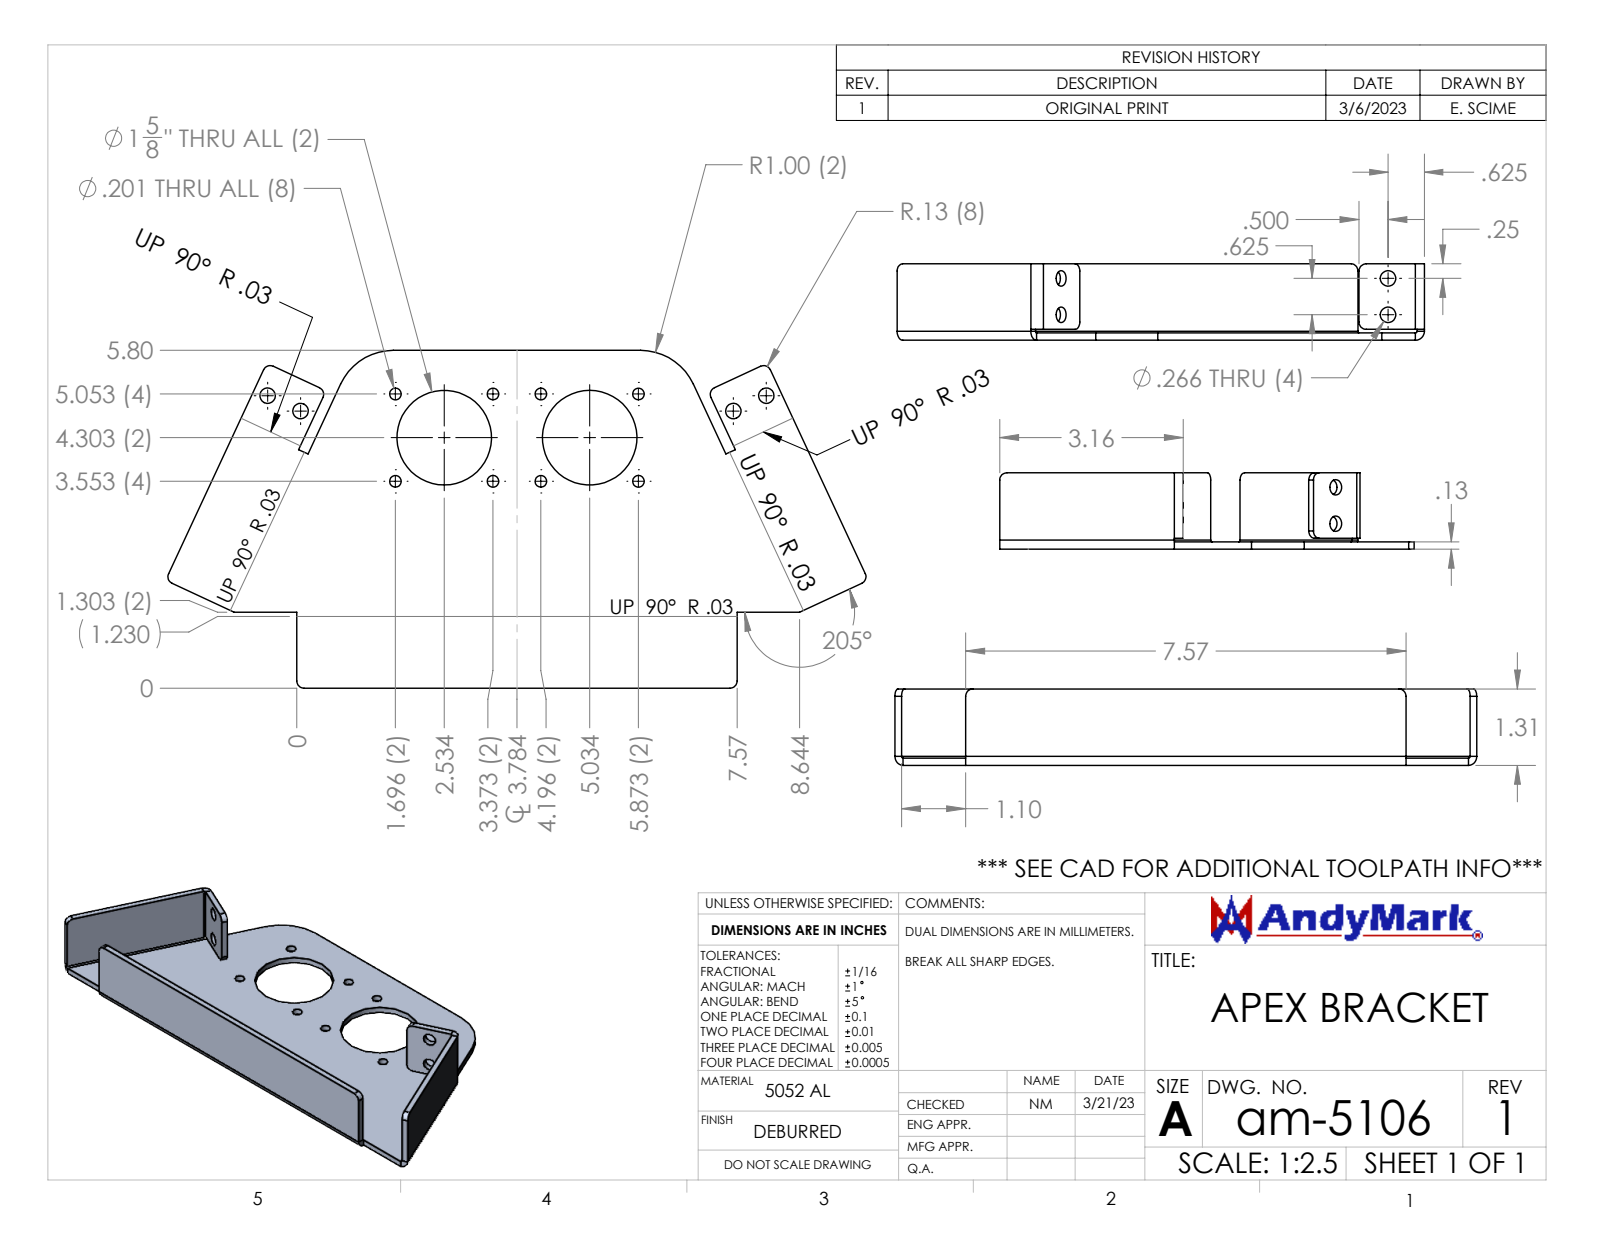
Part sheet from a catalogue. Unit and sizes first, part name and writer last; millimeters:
Units: millimetres
Overall size (bounding box): 254 × 118.2 × 33.4
Round holes (diameter × count): ⌀5.1 ×8, ⌀6.8 ×4, ⌀41.3 ×2
Partial cylindrical surfaces — rounded edges, fillets, slot ends (radius × count): R3.2 ×8, R0.8 ×5, R3.9 ×5, R25.4 ×2
Main face-to-face distances: 3.2, 3.2, 33.3, 30.1, 115.1, 118.2, 0.8, 3.9, 114.3, 4.7
Hole centre spacings: 28.6, 63.5, 38.1, 42.6, 46.3, 57.2, 74, 86.9
Volume: 101 800 mm³ · Surface area: 68 580 mm²
Bodies: 1 solid, 90 faces (42 planar, 48 cylindrical, 0 other)
Part name (STEP PRODUCT): am-5106 Apex Bracket
STEP written by: SolidWorks 2022 (AUTOMOTIVE_DESIGN)
